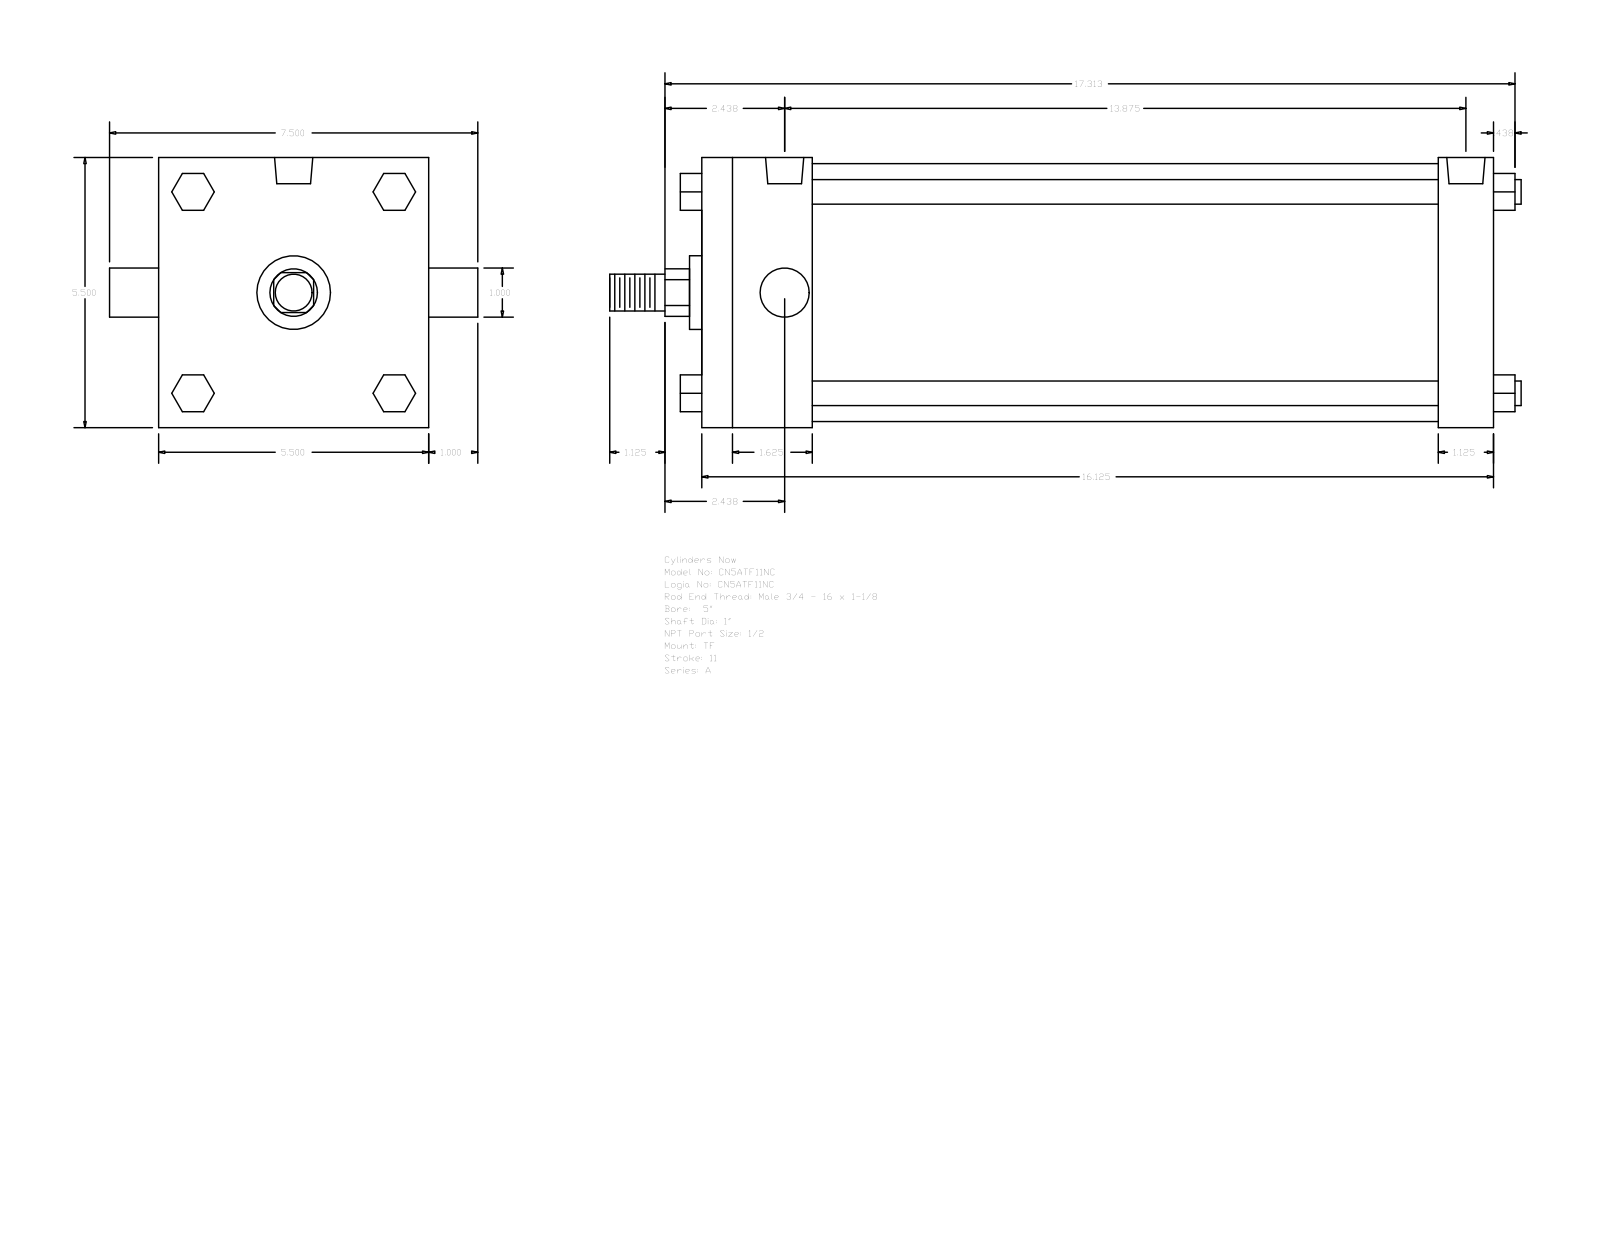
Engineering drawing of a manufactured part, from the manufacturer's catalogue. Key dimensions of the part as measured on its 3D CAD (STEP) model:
Part name (STEP PRODUCT): A_TF__0500_1
STEP written by: GSSL Pune (CONFIG_CONTROL_DESIGN)
Units: millimetres
Bodies: 0 solids, 120 faces (92 planar, 28 cylindrical, 0 other)
Overall size (bounding box): 471.49 × 190.5 × 139.7
Round holes (diameter × count): ⌀8.73 ×3, ⌀19.77 ×2
Round bosses / shafts (diameter × count): ⌀12.7 ×4, ⌀25.4 ×2, ⌀133.35 ×1, ⌀38.1 ×1, ⌀19.05 ×1
Partial cylindrical surfaces — rounded edges, fillets, slot ends (radius × count): R12.29 ×1
Main face-to-face distances: 139.7, 409.57, 28.57, 381, 57.15, 323.85, 352.42, 19.05, 52.07, 90.18
Hole centre spacings: 2.39, 350.04, 347.65, 352.43
